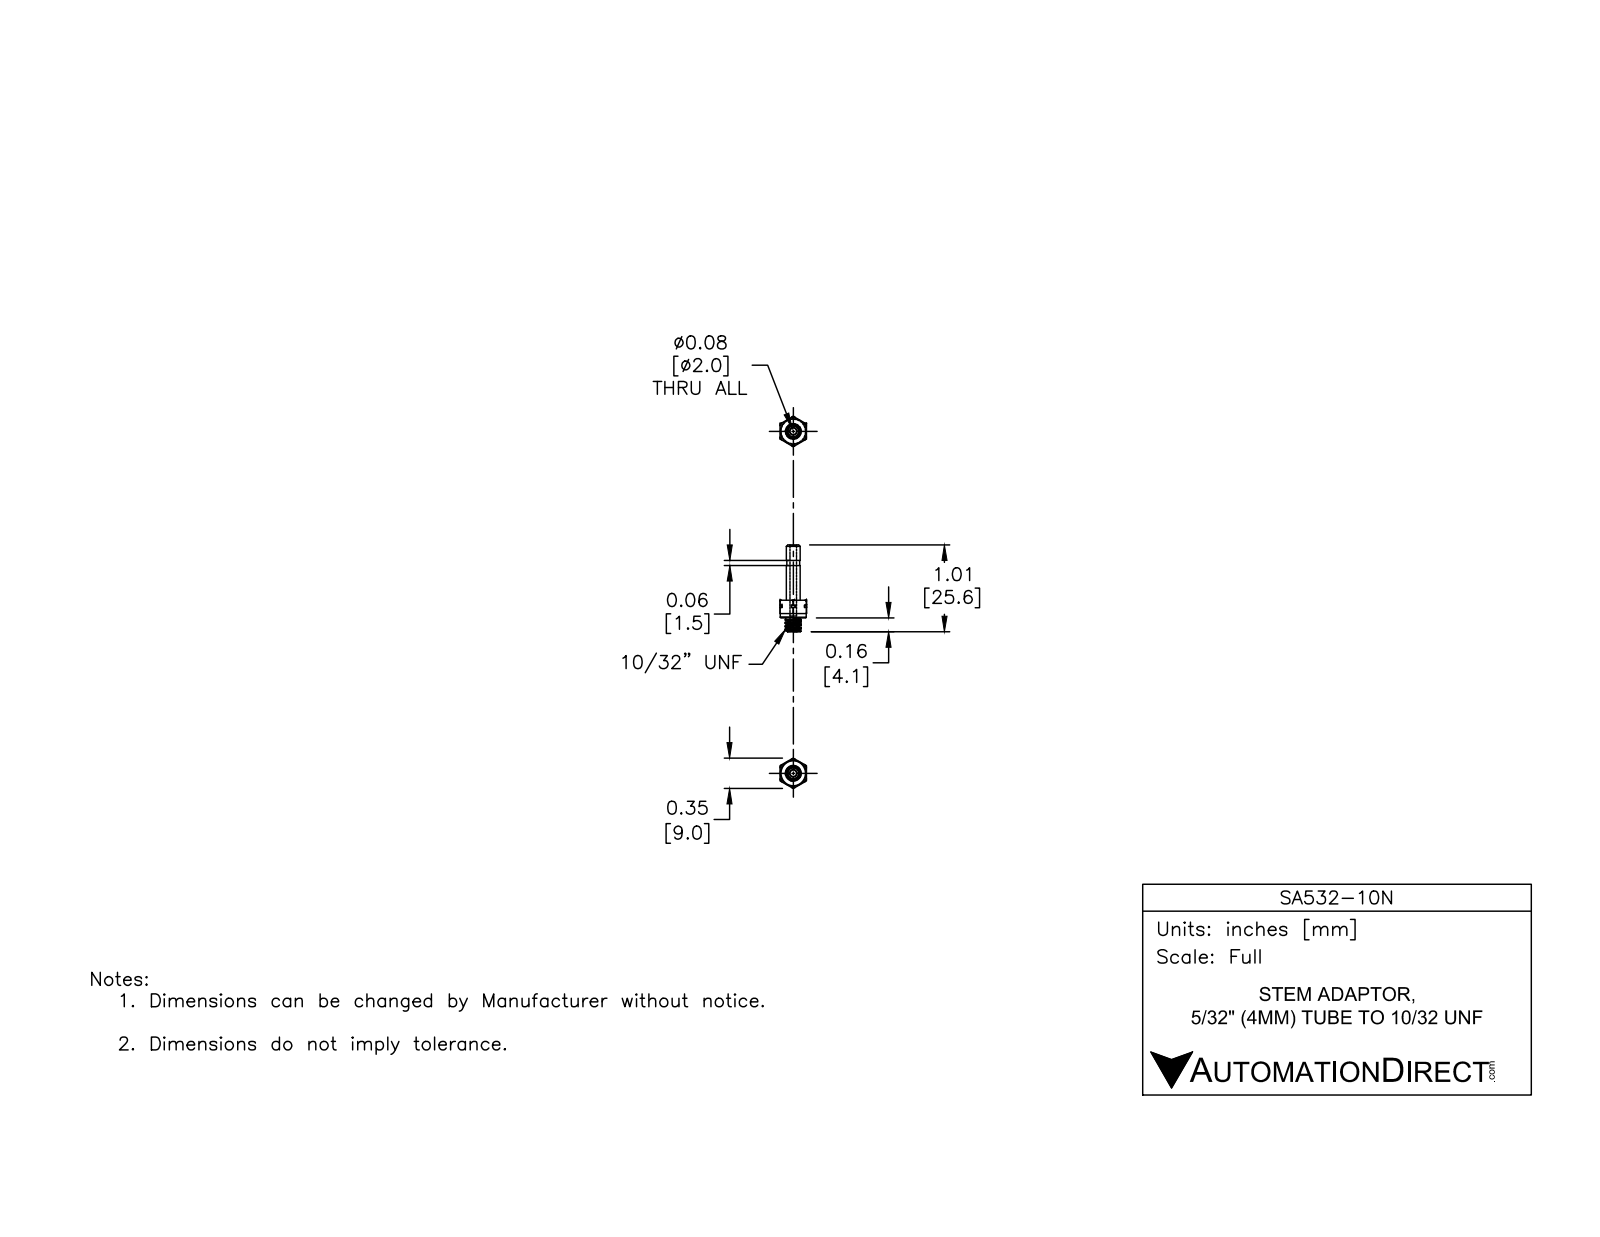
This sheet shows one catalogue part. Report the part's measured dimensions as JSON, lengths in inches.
{"part_name": "SA532-10N", "step_written_by": "SolidWorks 2015 (CONFIG_CONTROL_DESIGN)", "units": "inches", "bodies": {"solids": 2, "faces": 68, "planar": 14, "cylindrical": 32, "other": 22}, "overall_size": [1.022, 0.354, 0.311], "volume_in3": 0.029, "surface_area_in2": 1.2, "round_holes": [[0.089, 1]], "round_bosses_or_shafts": [[0.303, 1], [0.183, 1], [0.16, 1], [0.155, 1], [0.154, 1]], "partial_cylinders_radius": [[0.17, 1], [0.177, 1]], "face_to_face_distances": [0.311, 0.217, 0.167, 0.384, 0.207, 0.039, 0.177, 1.022, 0.854, 0.815]}
